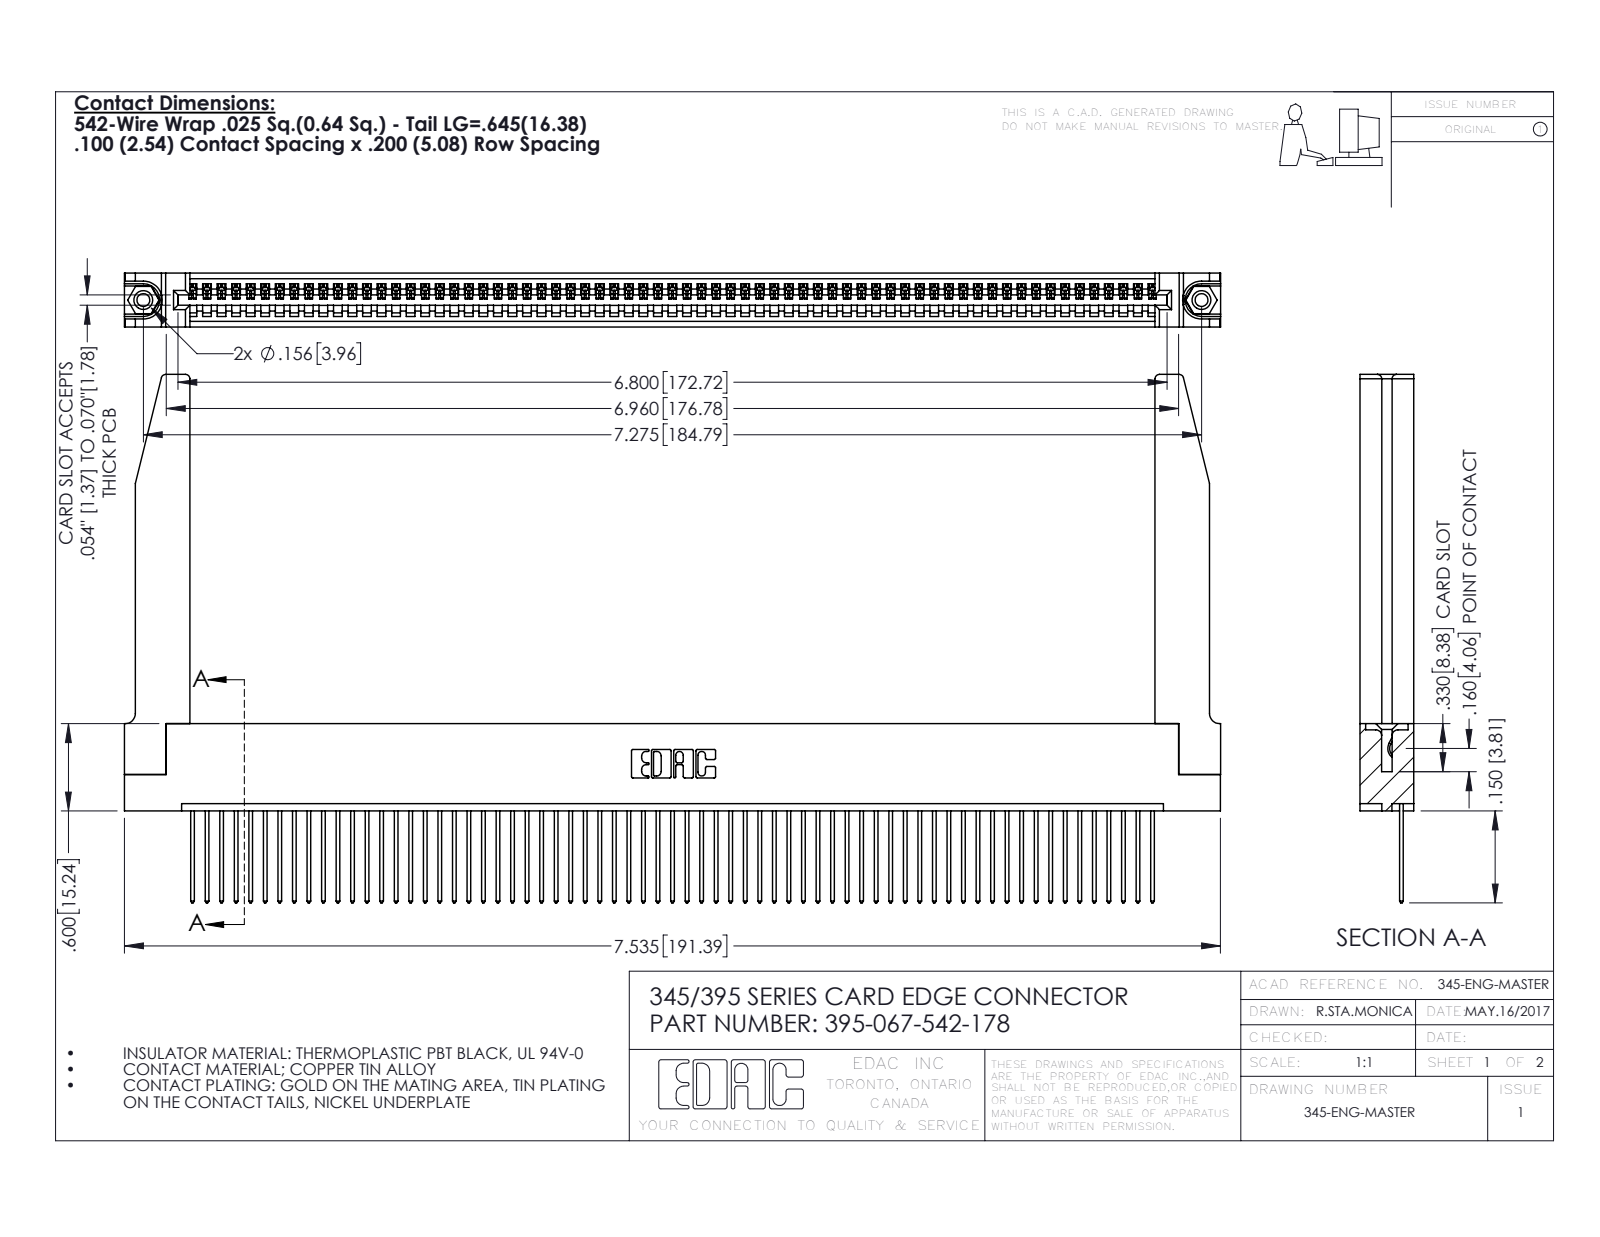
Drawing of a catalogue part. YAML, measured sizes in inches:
part_name: "345-220-078_345-220-078; 345 Part_Flush Mounting Lugs - 0.156 Dia-TH; 345-292-001_345-293-142; 345-250-001_345-250-001-102 (+1 more)"
step_written_by: "SolidWorks 2016 (CONFIG_CONTROL_DESIGN)"
units: inches
bodies: {solids: 72, faces: 4246, planar: 2902, cylindrical: 1292, other: 52}
overall_size: [7.536, 3.632, 0.37]
volume: 1.605
surface_area: 50.78
round_holes:
  - {diameter: 0.089, count: 2}
  - {diameter: 0.125, count: 2}
  - {diameter: 0.156, count: 2}
  - {diameter: 0.064, count: 1}
round_bosses_or_shafts:
  - {diameter: 0.155, count: 2}
partial_cylinders:
  - {radius: 0.006, count: 134}
  - {radius: 0.01, count: 134}
  - {radius: 0.01, count: 22}
  - {radius: 0.03, count: 8}
  - {radius: 0.007, count: 6}
  - {radius: 0.031, count: 6}
  - {radius: 0.026, count: 3}
  - {radius: 0.031, count: 2}
face_to_face_distances: [0.072, 0.298, 0.37, 0.098, 0.272, 0.025, 0.2, 0.225, 0.149, 0.148]
hole_center_spacings: [0.27, 7.039, 7.275]
